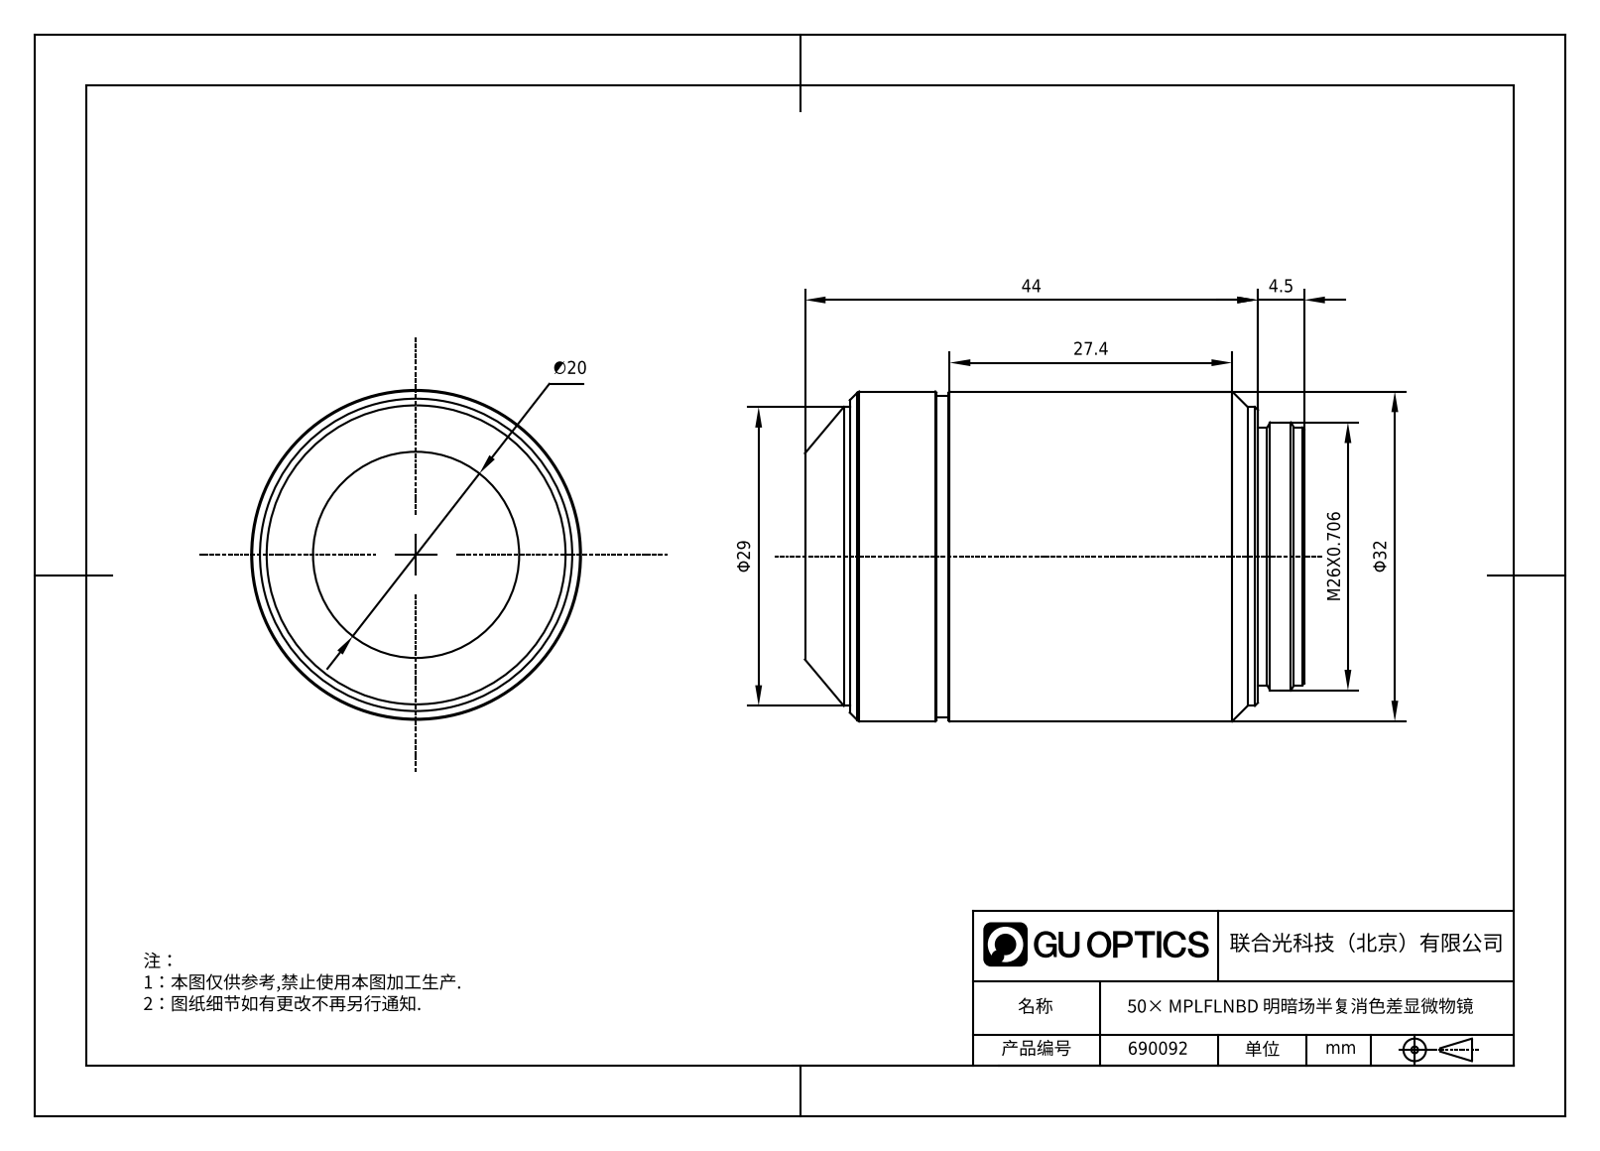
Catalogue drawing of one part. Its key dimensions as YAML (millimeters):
part_name: "690092.stp; 690092; MPLFLN50XBD.stp"
step_written_by: "SolidWorks 2020 (CONFIG_CONTROL_DESIGN)"
units: millimeters
bodies: {solids: 1, faces: 42, planar: 6, cylindrical: 16, other: 20}
overall_size: [48.45, 32, 32]
volume: 35985
surface_area: 6041
round_bosses_or_shafts:
  - {diameter: 32, count: 1}
  - {diameter: 31.2, count: 1}
  - {diameter: 29, count: 1}
  - {diameter: 26, count: 1}
  - {diameter: 25, count: 1}
face_to_face_distances: [48.45, 43.95, 4.5, 4.35, 39.6, 44.1, 12.75, 13.95, 8.4, 9.6]
